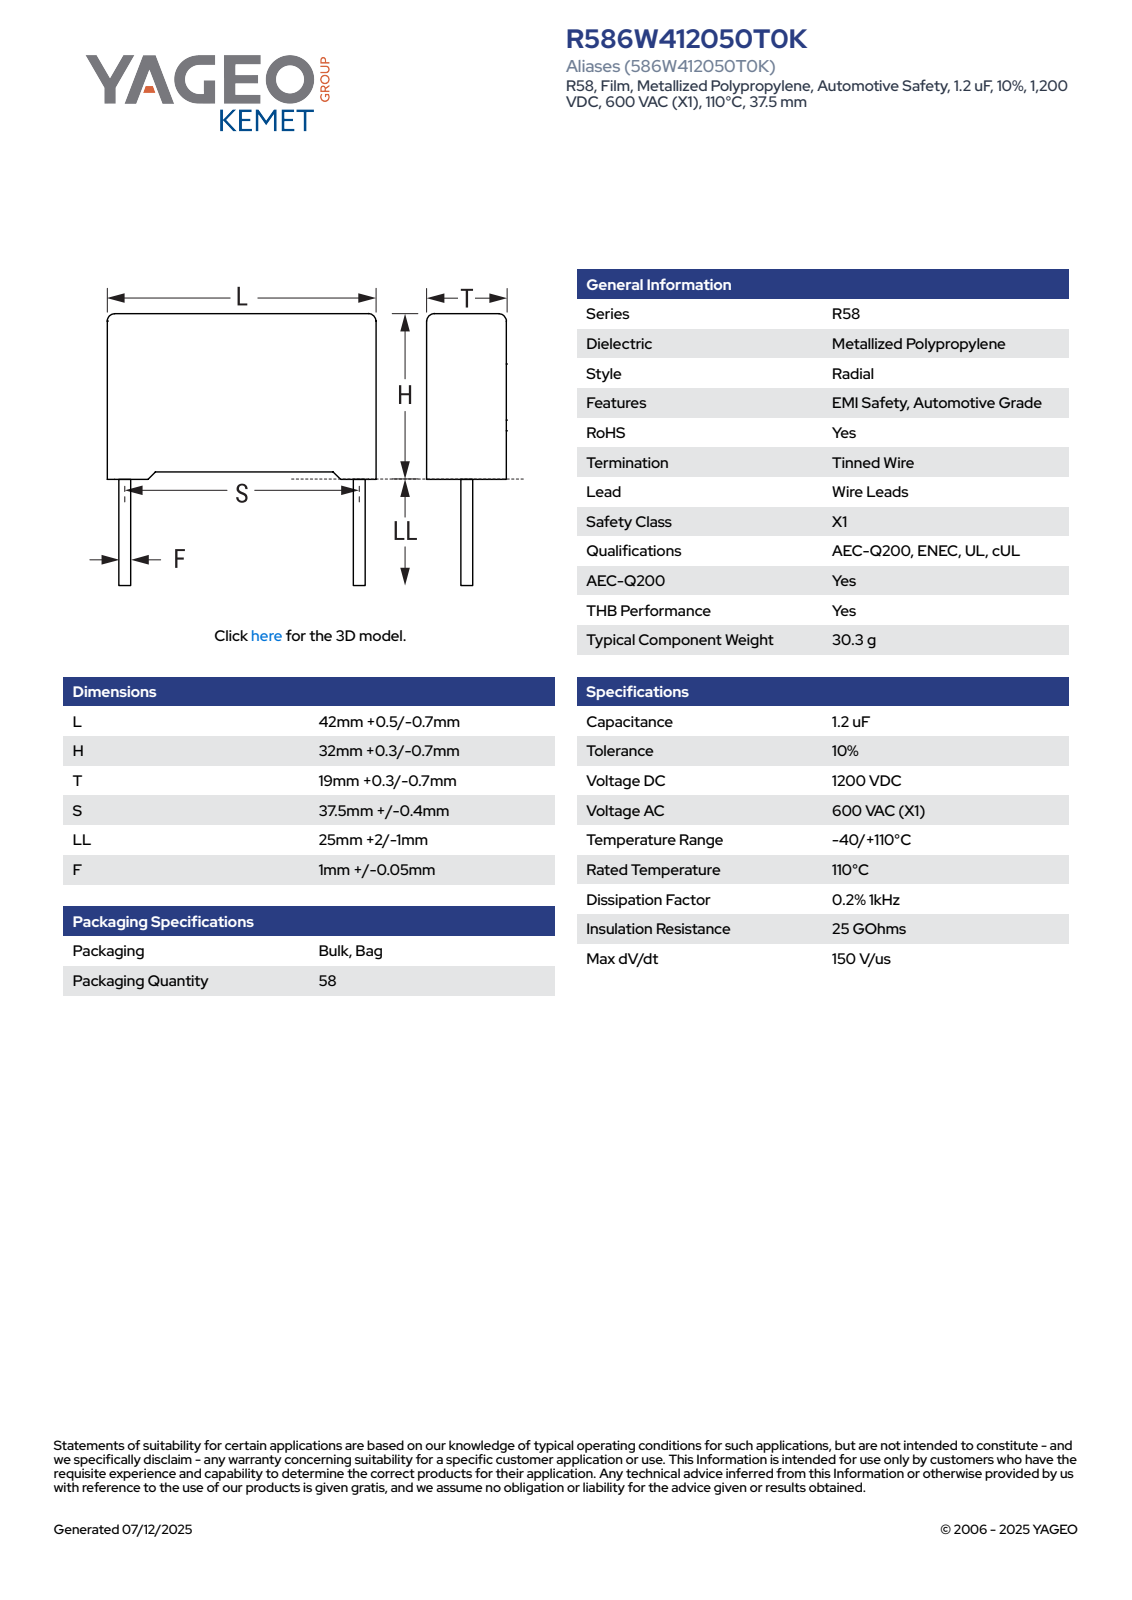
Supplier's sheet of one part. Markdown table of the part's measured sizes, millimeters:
| quantity | value |
| --- | --- |
| part name | CFR_RB2_42X32X19_L42.5H32.3T19.3S37.5LL27F1.05 |
| STEP written by | SolidWorks 2021 (AUTOMOTIVE_DESIGN) |
| units | millimeters |
| bodies | 4 solids, 85 faces (77 planar, 8 cylindrical, 0 other) |
| overall size | 59.3 × 42.5 × 19.3 |
| volume | 25 746 mm³ |
| surface area | 5 891 mm² |
| round bosses / shafts (diameter × count) | 1.05 × 2 |
| partial cylindrical surfaces (radius × count) | 0.5 × 4 |
| main face-to-face distances | 19.3, 31.19, 42.5, 0.36, 31.55, 0.75, 1.11, 32.3, 1.42, 19.31 |
